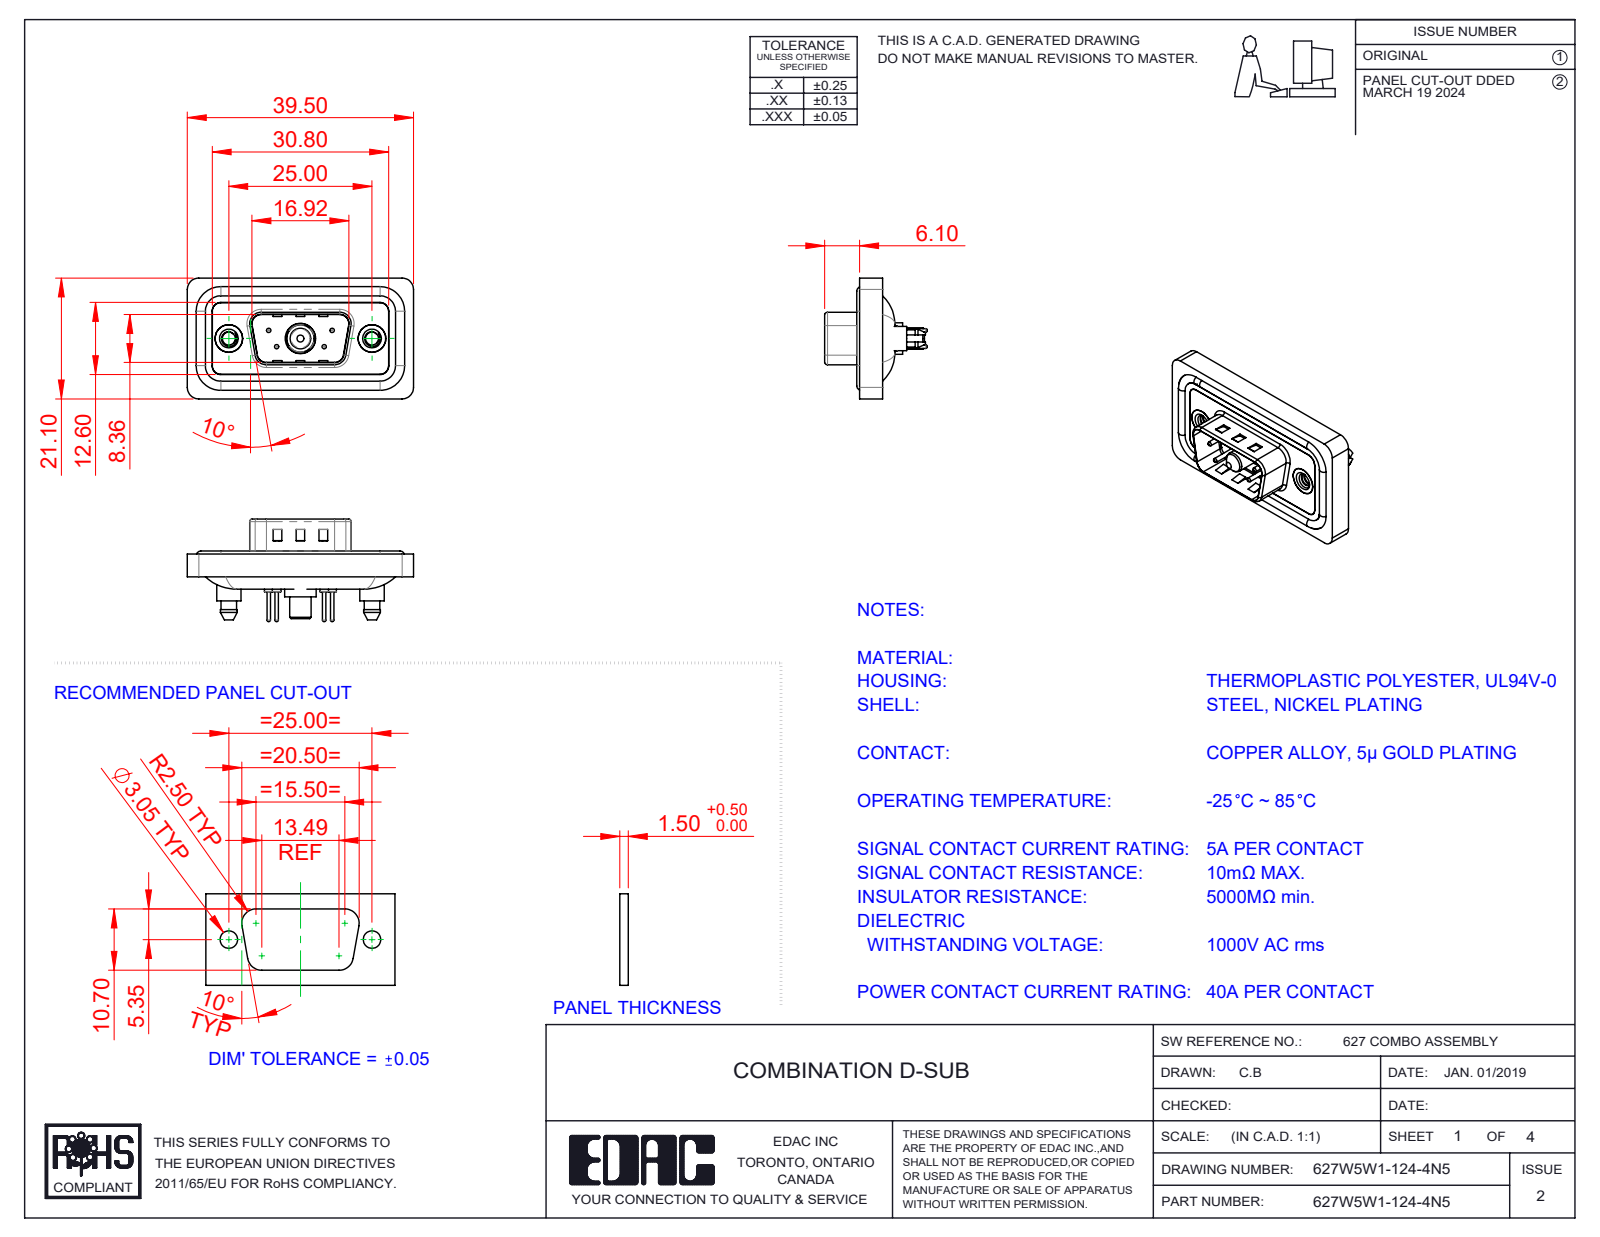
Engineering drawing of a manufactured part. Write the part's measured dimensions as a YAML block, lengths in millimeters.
part_name: "627Combo Shell Rear_09 Contacts; 627Combo Housing_5W1; 627W5W1-124-4N5; Power Pin_40A S (+5 more)"
step_written_by: "SolidWorks 2023 (CONFIG_CONTROL_DESIGN)"
units: millimeters
bodies: {solids: 13, faces: 648, planar: 199, cylindrical: 287, other: 162}
overall_size: [39.5, 21.1, 17.9]
volume: 4540
surface_area: 7285
round_holes:
  - {diameter: 0.75, count: 4}
  - {diameter: 1.6, count: 4}
  - {diameter: 2, count: 4}
  - {diameter: 2.26, count: 2}
  - {diameter: 4, count: 2}
  - {diameter: 4.8, count: 2}
  - {diameter: 5, count: 2}
  - {diameter: 4.85, count: 1}
  - {diameter: 5.3, count: 1}
round_bosses_or_shafts:
  - {diameter: 1.6, count: 4}
  - {diameter: 1.5, count: 4}
  - {diameter: 0.6, count: 4}
  - {diameter: 5.4, count: 2}
  - {diameter: 4.9, count: 2}
  - {diameter: 4.25, count: 2}
  - {diameter: 5.5, count: 1}
  - {diameter: 5.2, count: 1}
partial_cylinders:
  - {radius: 1.5, count: 24}
  - {radius: 2, count: 18}
  - {radius: 1.6, count: 10}
  - {radius: 0.5, count: 8}
  - {radius: 0.25, count: 4}
  - {radius: 0.6, count: 4}
  - {radius: 0.65, count: 4}
  - {radius: 0.9, count: 4}
face_to_face_distances: [0.4, 1.1, 2.9, 1.6, 3.1, 1.5, 0.5, 2.5, 4, 0.8]
hole_center_spacings: [3.16, 5.72, 7.1, 12.5, 18.1, 4.39, 4.4, 8.31]
